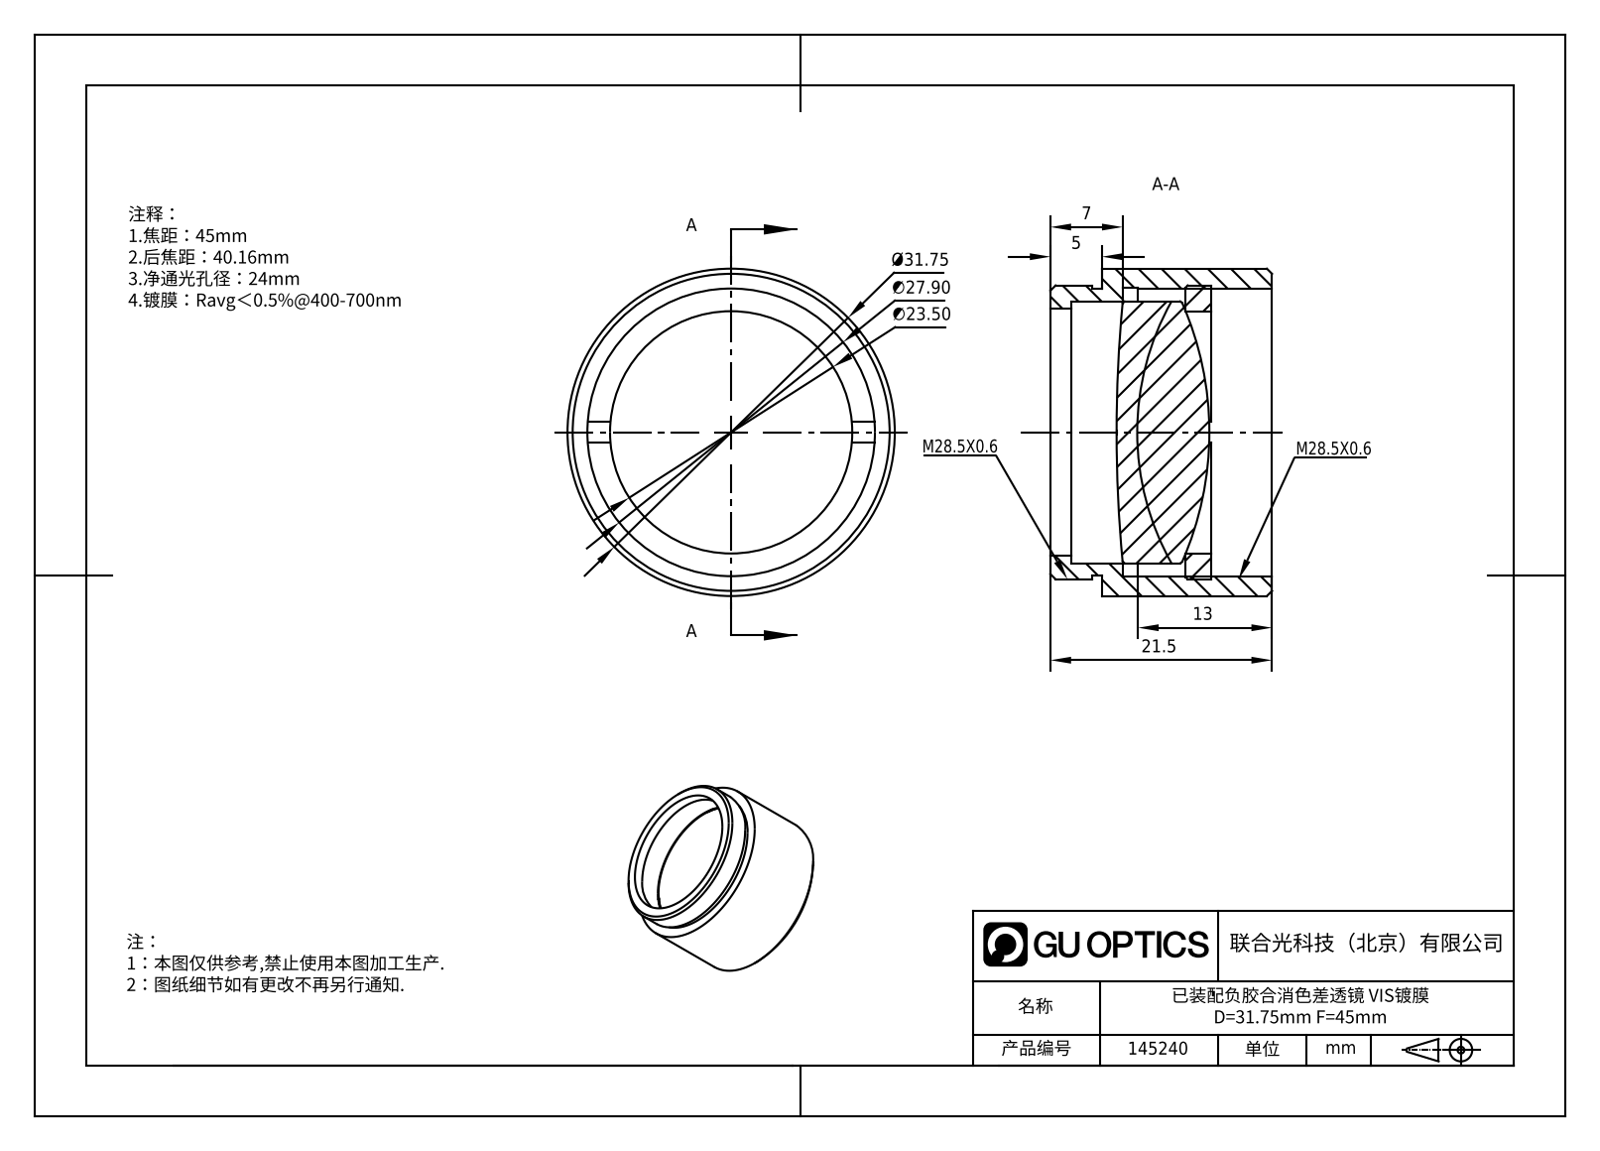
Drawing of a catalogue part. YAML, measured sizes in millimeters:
part_name: "GL31-025B-045-VIS_Solidworks; M28.5x0.6ѹȦ; M28.5x0.6安装环PN35021-LM254-D2; APD-ML25-045-VIS"
step_written_by: "SolidWorks 2022 (AUTOMOTIVE_DESIGN)"
units: millimeters
bodies: {solids: 4, faces: 56, planar: 16, cylindrical: 22, other: 18}
overall_size: [31.76, 31.76, 21.5]
volume: 8129
surface_area: 7979
round_holes:
  - {diameter: 23.5, count: 1}
  - {diameter: 24, count: 1}
  - {diameter: 27.9, count: 1}
  - {diameter: 28, count: 1}
round_bosses_or_shafts:
  - {diameter: 31.76, count: 1}
  - {diameter: 28.5, count: 1}
  - {diameter: 27.8, count: 1}
  - {diameter: 25.4, count: 1}
face_to_face_distances: [2, 5, 2.5, 8.12, 10.62, 13.12, 15.62, 21.5, 16.5, 8.38]
